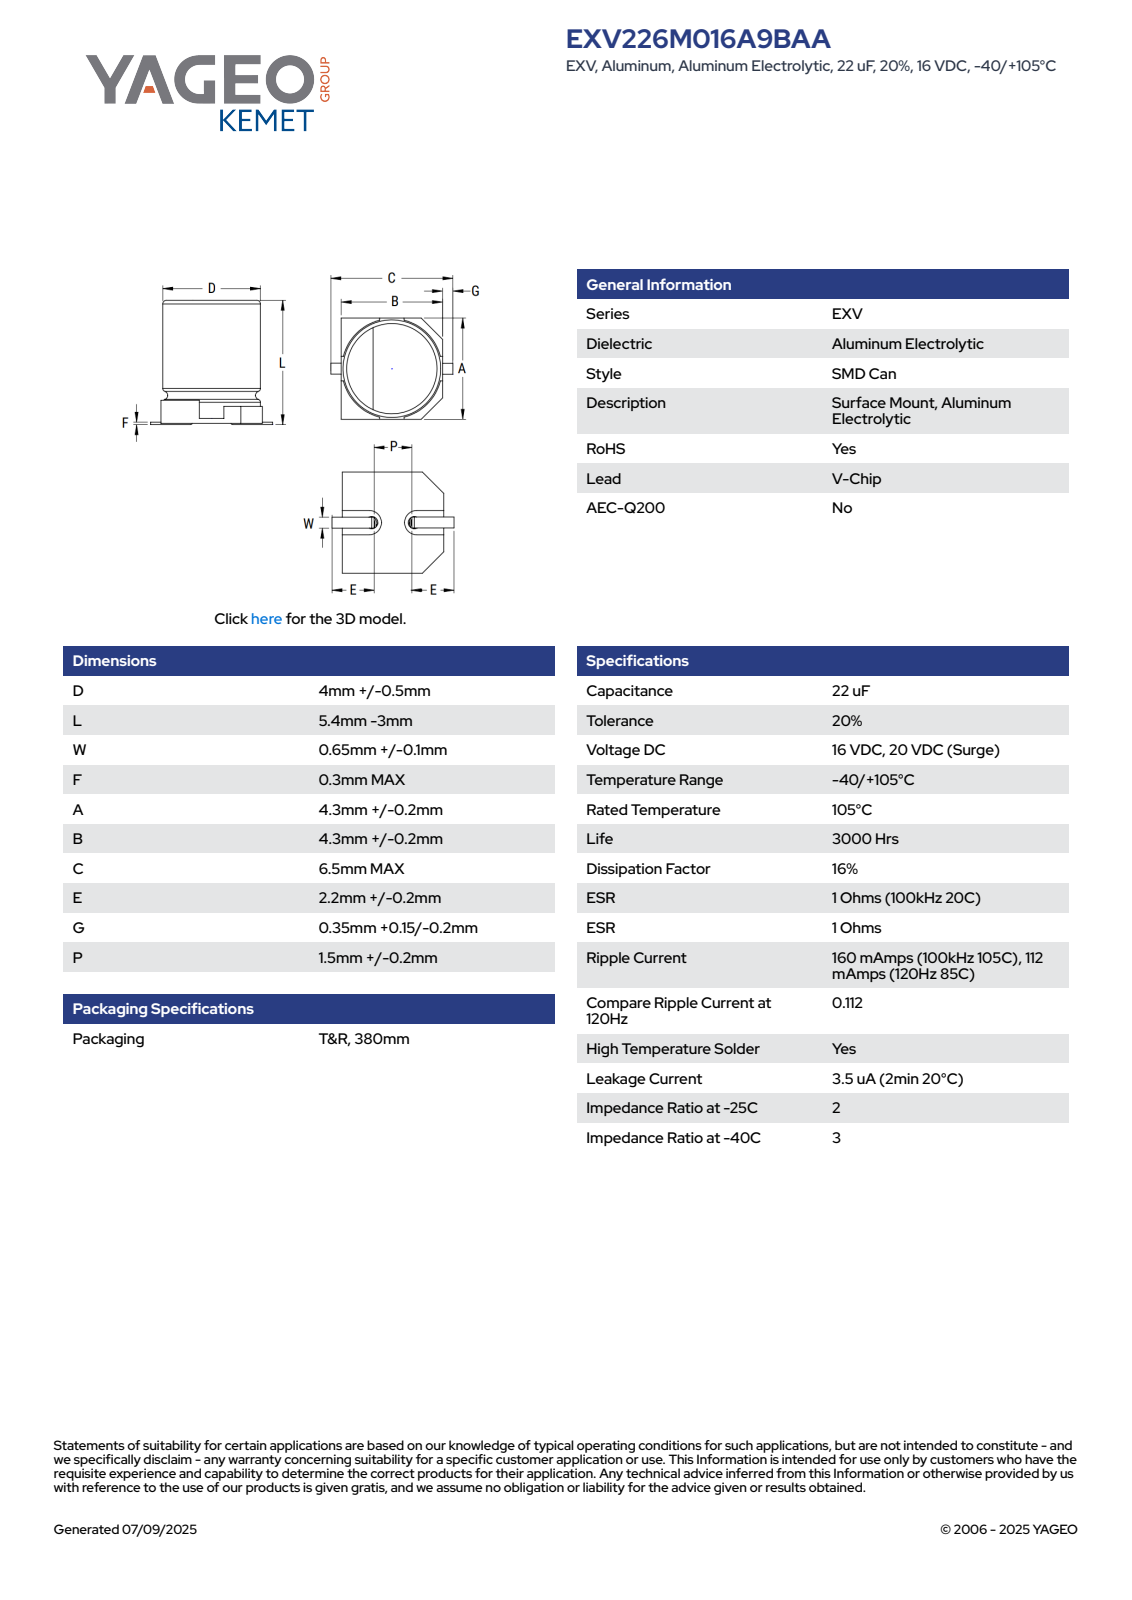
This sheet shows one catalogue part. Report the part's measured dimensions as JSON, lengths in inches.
{"part_name": "CAC_S_4X5.4_D4.5L5.65W0.75F0.3A4.5B4.5C6.5E2.4P1.7", "step_written_by": "SolidWorks 2021 (AUTOMOTIVE_DESIGN)", "units": "inches", "bodies": {"solids": 5, "faces": 78, "planar": 61, "cylindrical": 11, "other": 6}, "overall_size": [0.256, 0.177, 0.094], "volume_in3": 0.002, "surface_area_in2": 0.172, "round_bosses_or_shafts": [[0.169, 1]], "partial_cylinders_radius": [[0.008, 2], [0.07, 1], [0.089, 1]], "face_to_face_distances": [0.083, 0.078, 0.094, 0.017, 0.059, 0.024, 0.035, 0.019, 0.03, 0.177]}
